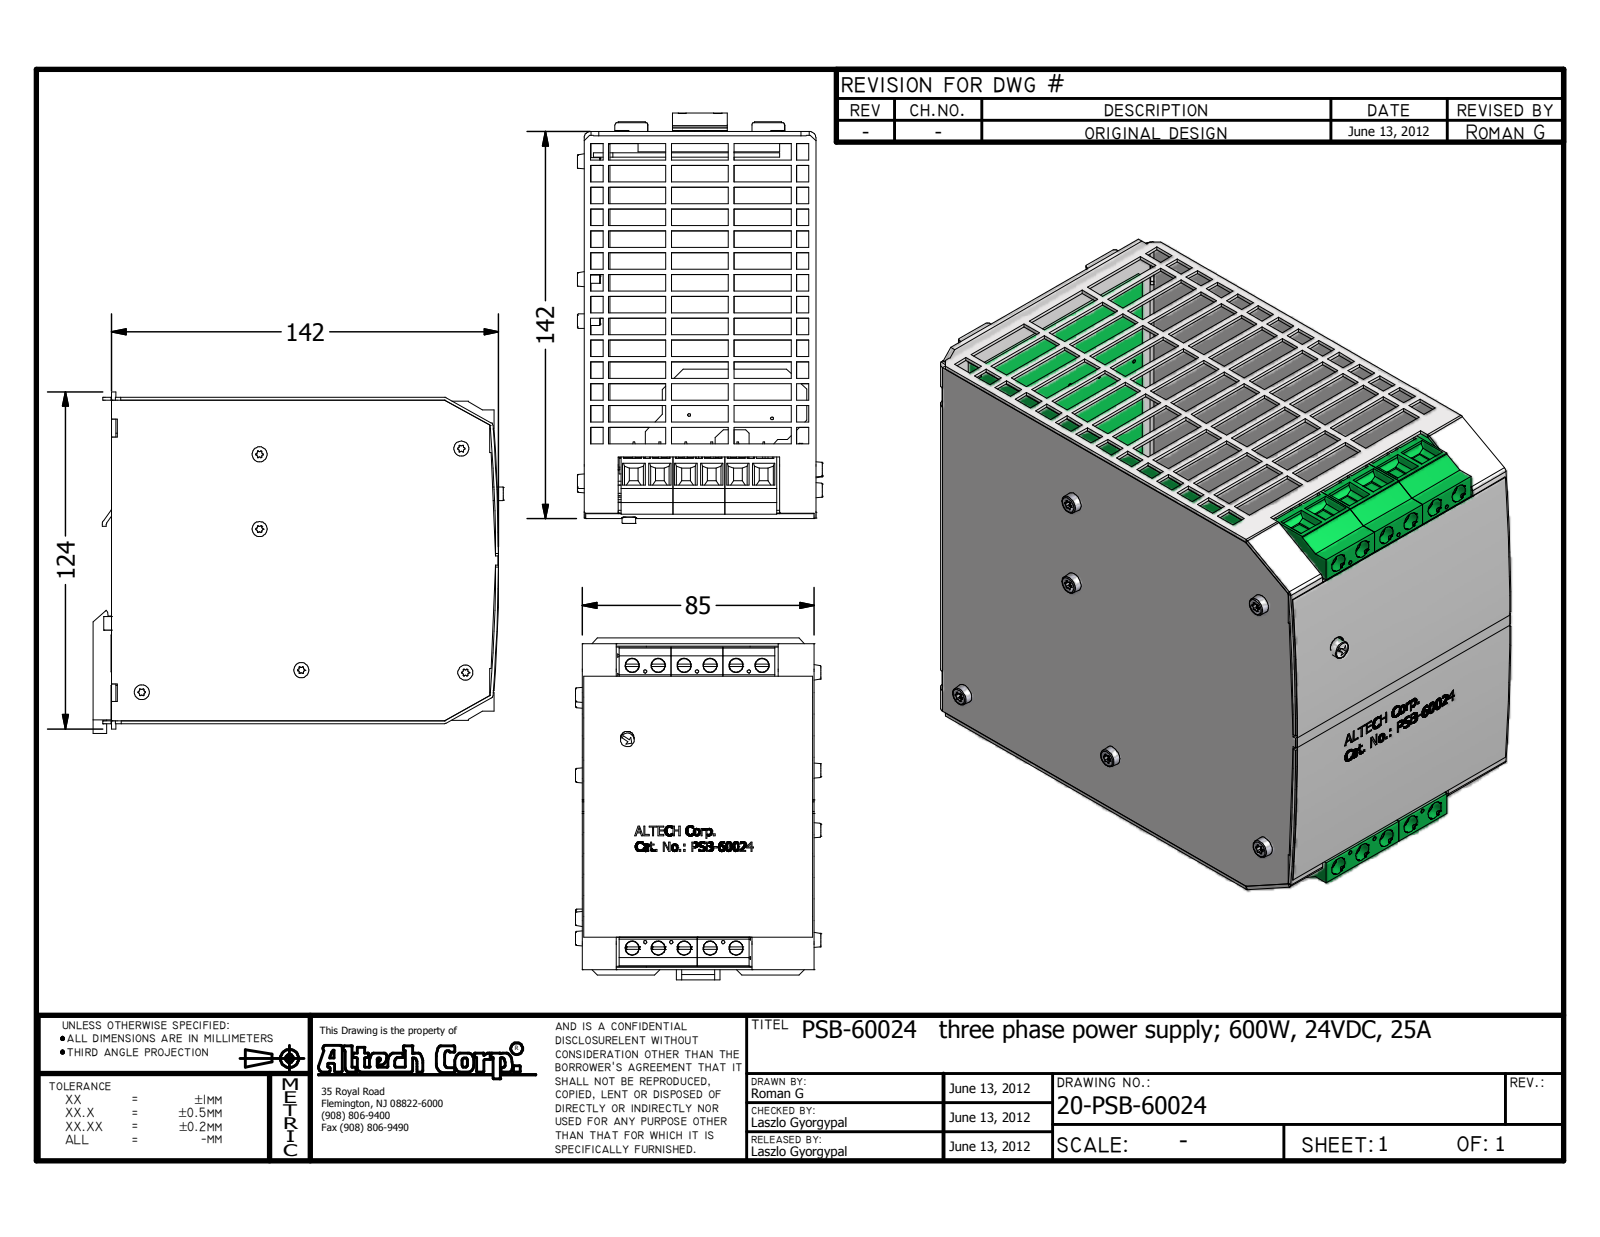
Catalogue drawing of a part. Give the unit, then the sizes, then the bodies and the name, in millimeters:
Units: millimetres
Overall size (bounding box): 150.5 × 125.2 × 89.8
Round holes (diameter × count): ⌀1 ×80, ⌀5.2 ×11, ⌀2.3 ×8, ⌀3.3 ×7, ⌀1.2 ×6, ⌀0.9 ×4, ⌀2.8 ×4, ⌀3.1 ×4, ⌀2 ×2, ⌀2.2 ×2, ⌀3.5 ×2
Round bosses / shafts (diameter × count): ⌀5 ×12, ⌀1.3 ×11, ⌀3 ×10, ⌀2.7 ×7, ⌀6.7 ×2, ⌀4.7 ×2, ⌀1.5 ×2, ⌀9 ×1
Partial cylindrical surfaces — rounded edges, fillets, slot ends (radius × count): R0.3 ×61, R0.6 ×60, R0.1 ×44, R0.2 ×17, R0.6 ×16, R1.2 ×14, R1 ×10, R0.5 ×8
Main face-to-face distances: 1.5, 83.5, 1.6, 85, 82, 7.9, 6.4, 75.6, 77.1, 9.5
Hole centre spacings: 5.2, 100.7, 9.5, 19.1, 102.4, 14.5, 101.5, 104.1
Volume: 173 700 mm³ · Surface area: 209 700 mm²
Bodies: 3 solids, 3252 faces (2385 planar, 549 cylindrical, 318 other)
Part name (STEP PRODUCT): ALTECH-PSB-60024
STEP written by: Autodesk Inventor 2013 (CONFIG_CONTROL_DESIGN)
